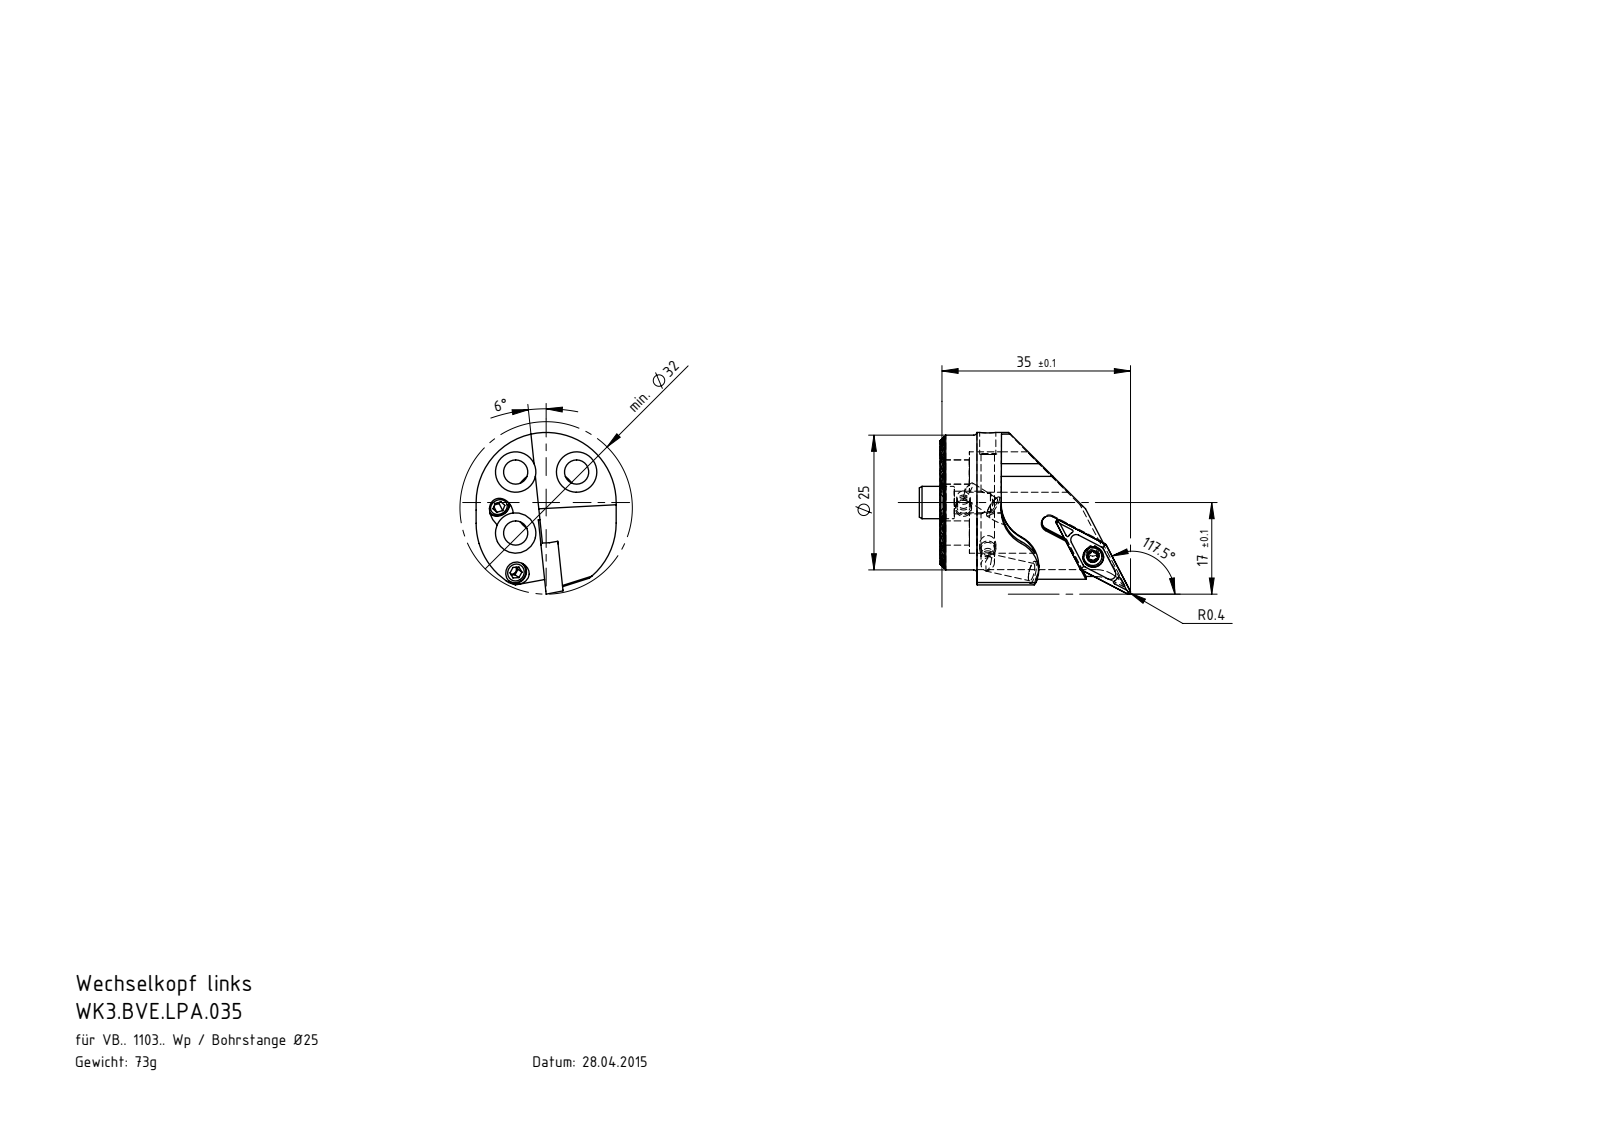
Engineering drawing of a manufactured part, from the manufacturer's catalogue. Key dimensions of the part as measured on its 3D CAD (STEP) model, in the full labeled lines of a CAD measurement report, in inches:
Part name (STEP PRODUCT): WK3-BVE.LPA.035_A; WCA-ER2.001.006_A; WKX-ER1.004.005_A_PreviewCfg; WK3.BVE.LPA.035 (+3 more)
STEP written by: SolidWorks 2017 (AUTOMOTIVE_DESIGN)
Units: inches
Bodies: 12 solids, 387 faces (185 planar, 96 cylindrical, 106 other)
Overall size (bounding box): 1.543 × 1.181 × 1.024
Volume: 0.556 in³ · Surface area: 9.576 in²
Round holes (diameter × count): ⌀0.094 ×3, ⌀0.098 ×3, ⌀0.165 ×3, ⌀0.177 ×3, ⌀0.295 ×3, ⌀0.067 ×2, ⌀0.118 ×2, ⌀0.13 ×2, ⌀0.081 ×1, ⌀0.11 ×1, ⌀0.152 ×1, ⌀0.236 ×1
Round bosses / shafts (diameter × count): ⌀0.118 ×3, ⌀0.157 ×2, ⌀0.984 ×1, ⌀0.472 ×1, ⌀0.134 ×1, ⌀0.098 ×1
Partial cylindrical surfaces — rounded edges, fillets, slot ends (radius × count): R0.005 ×20, R0.008 ×6, R0.014 ×5, R0.512 ×3, R0.276 ×2, R0.014 ×1, R0.053 ×1, R0.236 ×1
Main face-to-face distances: 0.17, 0.043, 0.128, 0.213, 0.341, 0.298, 0.085, 0.085, 0.256, 0.383
Hole centre spacings: 0.315, 0.446, 0.63
